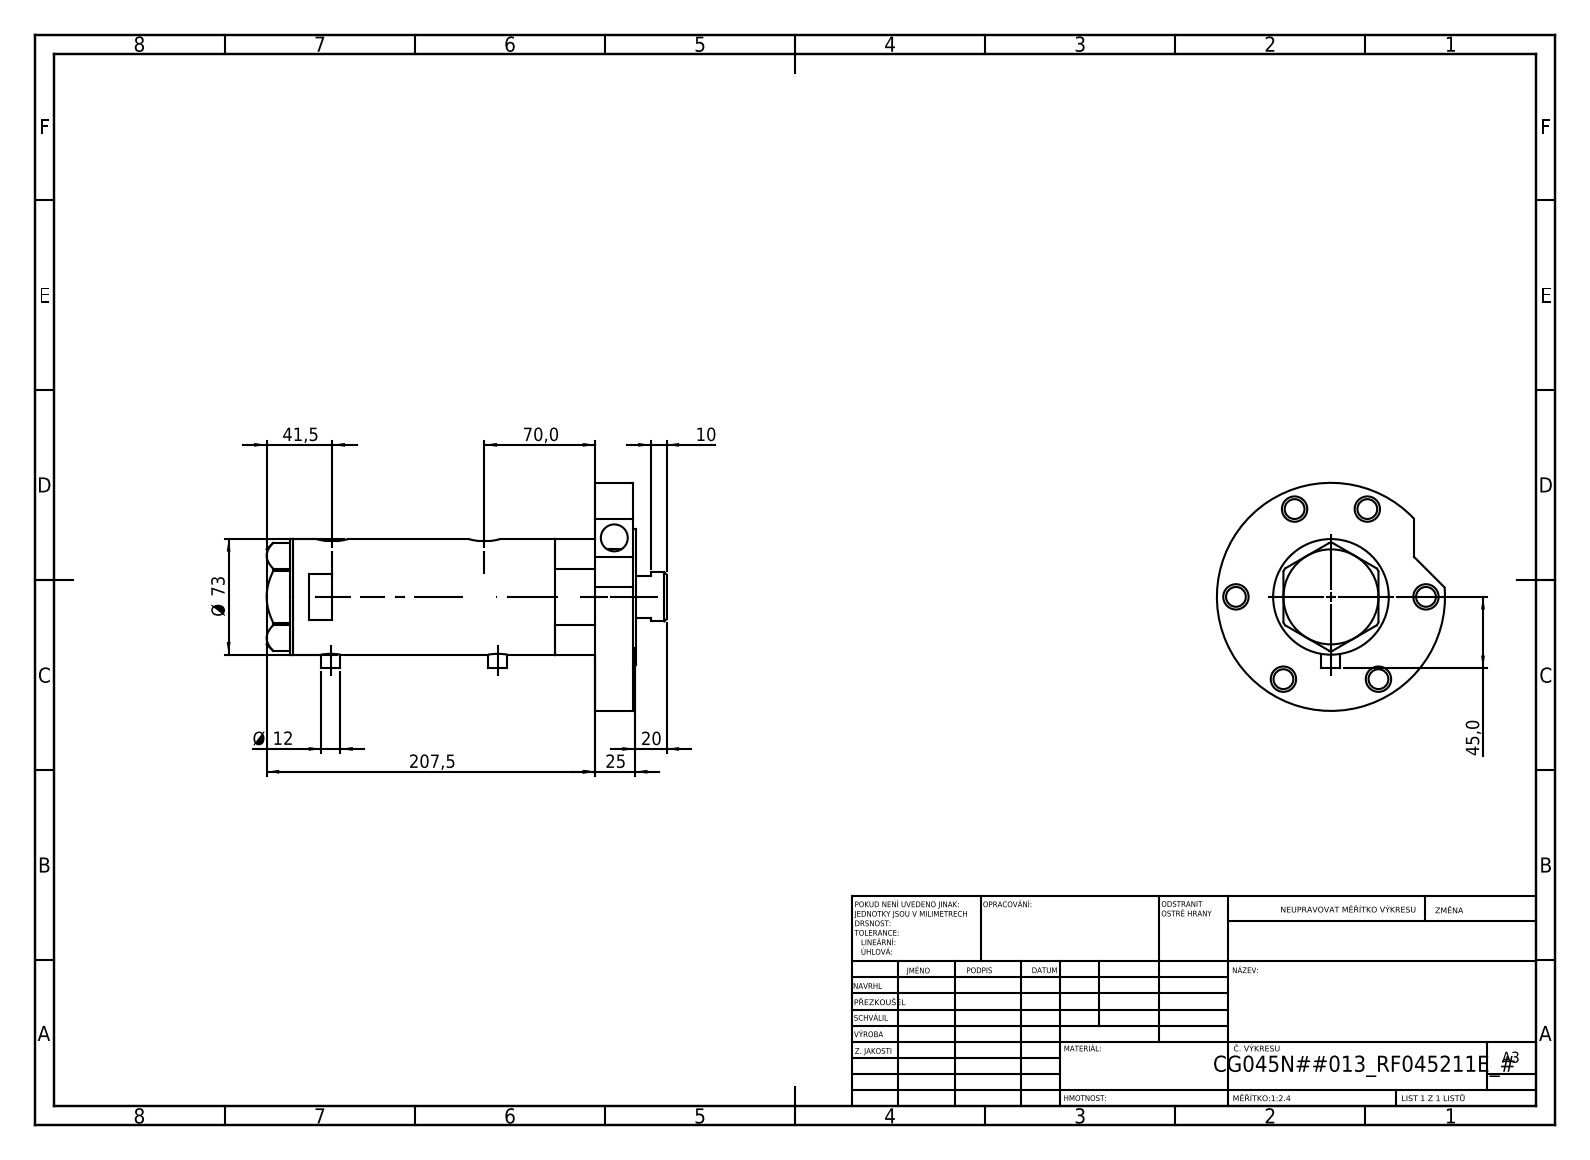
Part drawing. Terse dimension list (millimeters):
name: V270CG_BACK; V270CG_FRONT; V270CG_VC; V270CG_RF211E (+1 more)
written by: SolidWorks 2019 (CONFIG_CONTROL_DESIGN)
unit: mm
bodies: 5 solids, 164 faces (60 planar, 84 cylindrical, 20 other)
size: 252.5 × 144 × 144
volume: 1 189 000 mm³; area: 202 973 mm²
holes: 8× ⌀12.5, 6× ⌀16, 2× ⌀13.16, 1× ⌀10.5, 1× ⌀17, 1× ⌀32, 1× ⌀33.5, 1× ⌀45, 1× ⌀48, 1× ⌀60, 1× ⌀64
bosses: 2× ⌀12, 1× ⌀144, 1× ⌀86, 1× ⌀73, 1× ⌀58, 1× ⌀31
rounds: 2× R10
face distances: 24, 191, 26, 95, 2, 215, 217, 121, 70, 94
hole spacings: 60, 66.67, 99.77, 103.92, 107.62, 119.74, 1, 8.5
